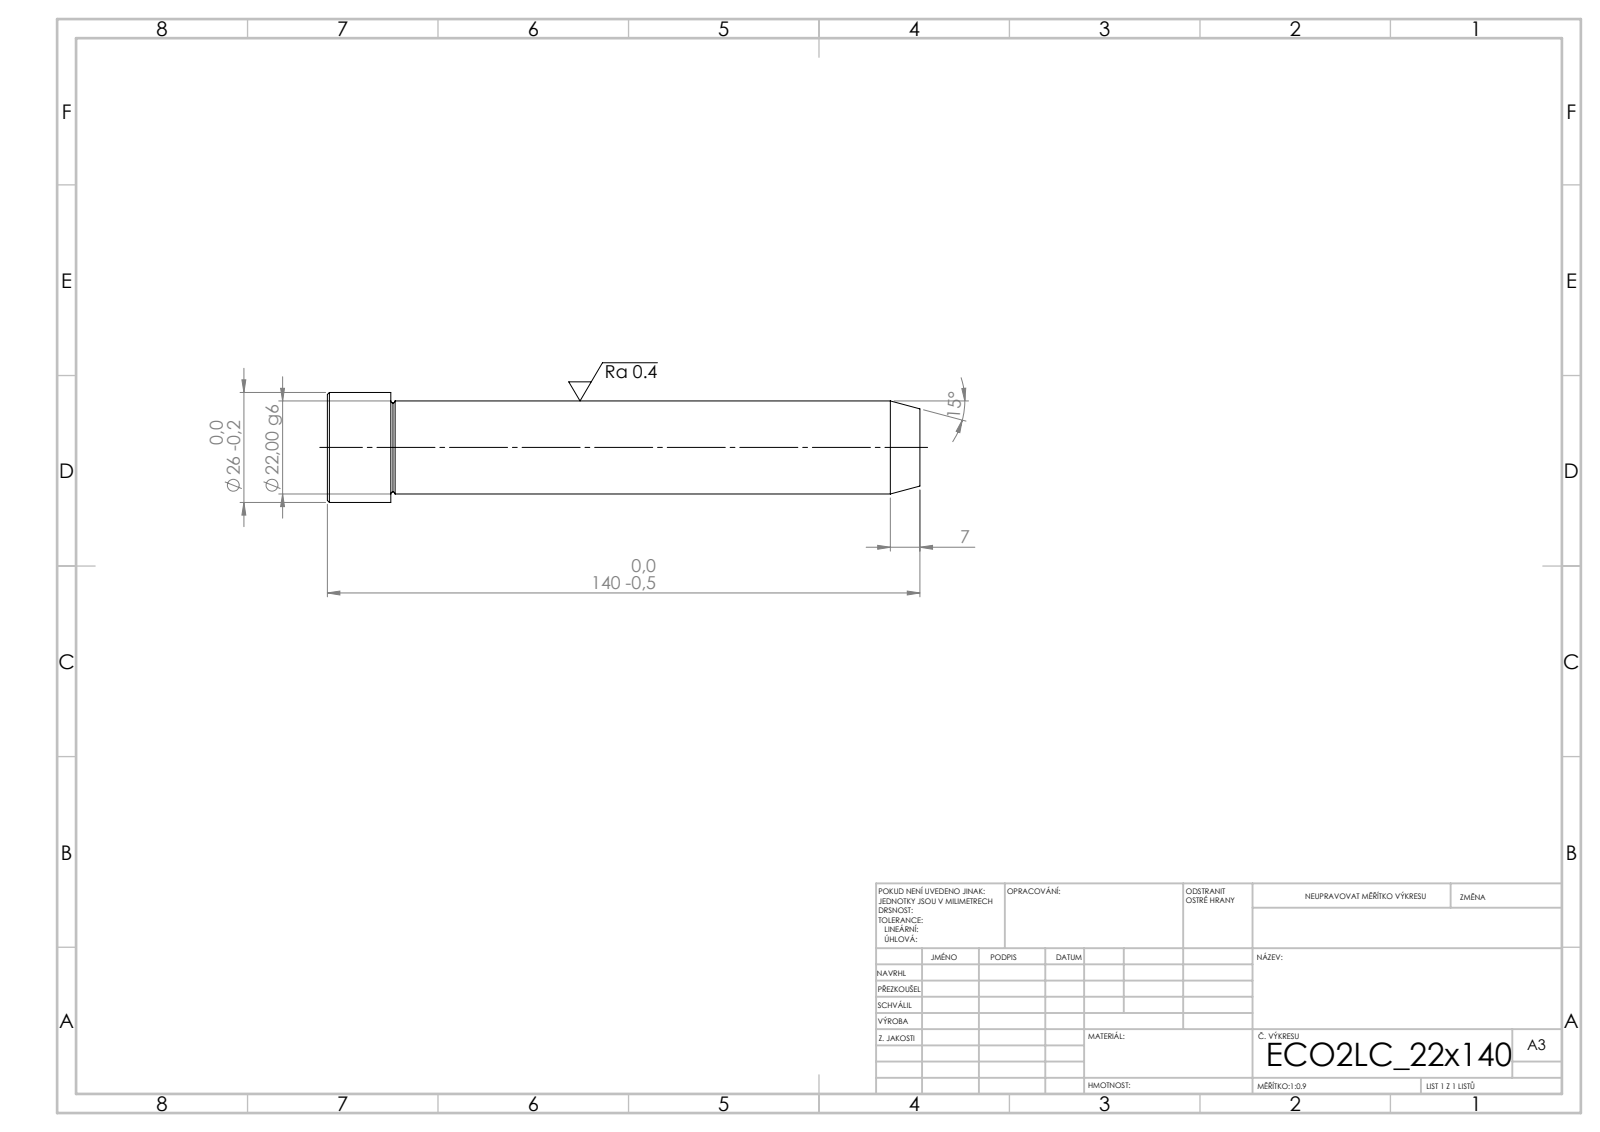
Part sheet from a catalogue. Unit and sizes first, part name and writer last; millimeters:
Units: millimetres
Overall size (bounding box): 140 × 26 × 26
Round bosses / shafts (diameter × count): ⌀26 ×1, ⌀22 ×1
Main face-to-face distances: 140, 125, 15
Volume: 55 016 mm³ · Surface area: 10 794 mm²
Bodies: 1 solid, 15 faces (3 planar, 4 cylindrical, 8 other)
STEP written by: SolidWorks 2019 (CONFIG_CONTROL_DESIGN)
